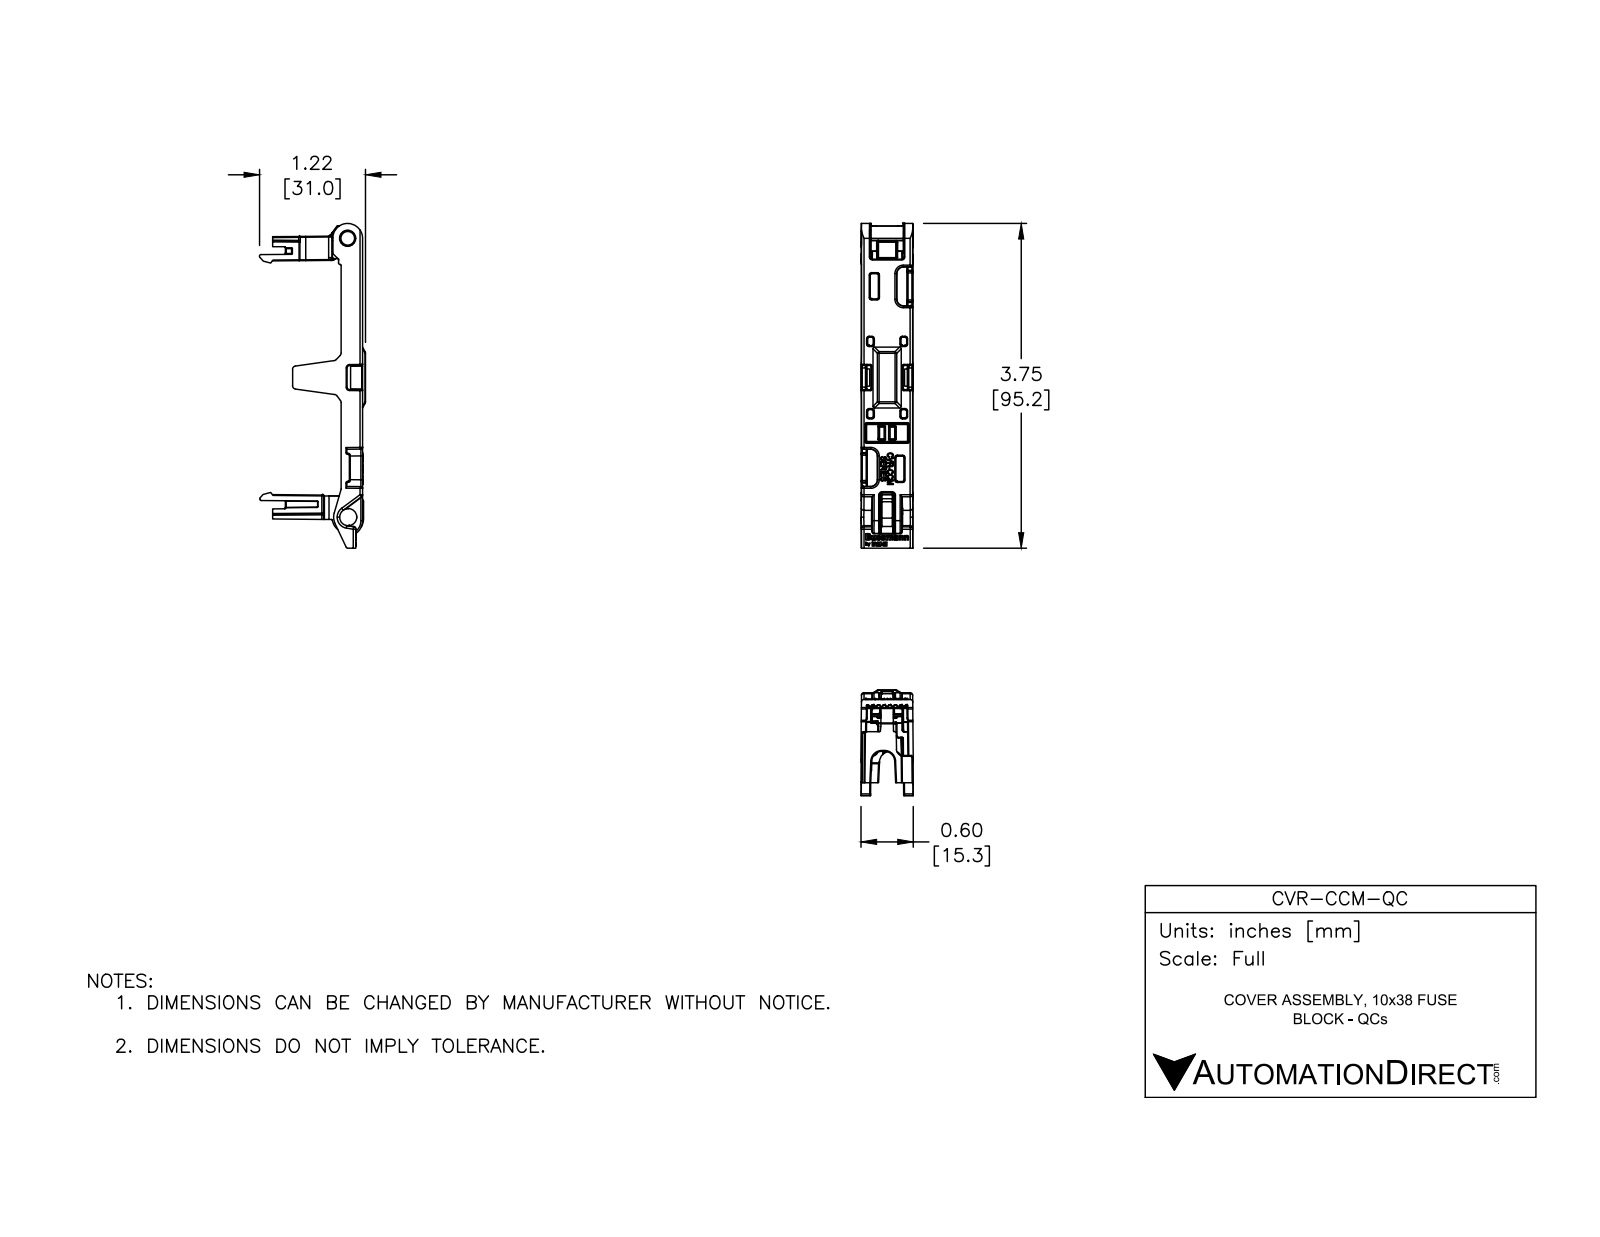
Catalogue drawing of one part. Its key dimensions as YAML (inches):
part_name: "CVR-CCM-QC"
step_written_by: "SolidWorks 2016 (AUTOMOTIVE_DESIGN)"
units: inches
bodies: {solids: 3, faces: 2408, planar: 631, cylindrical: 863, other: 914}
overall_size: [3.748, 1.222, 0.605]
volume: 0.395
surface_area: 13.67
round_holes:
  - {diameter: 0.157, count: 1}
  - {diameter: 0.185, count: 1}
  - {diameter: 0.197, count: 1}
round_bosses_or_shafts:
  - {diameter: 0.177, count: 1}
  - {diameter: 0.15, count: 1}
partial_cylinders:
  - {radius: 0.01, count: 261}
  - {radius: 0.006, count: 154}
  - {radius: 0.004, count: 147}
  - {radius: 0.02, count: 66}
  - {radius: 0.03, count: 18}
  - {radius: 0.039, count: 17}
  - {radius: 0.067, count: 7}
  - {radius: 0.079, count: 4}
face_to_face_distances: [0.061, 0.061, 0.247, 0.186, 0.185, 0.114, 0.08, 0.222, 0.281, 0.382]
hole_center_spacings: [3.219]
